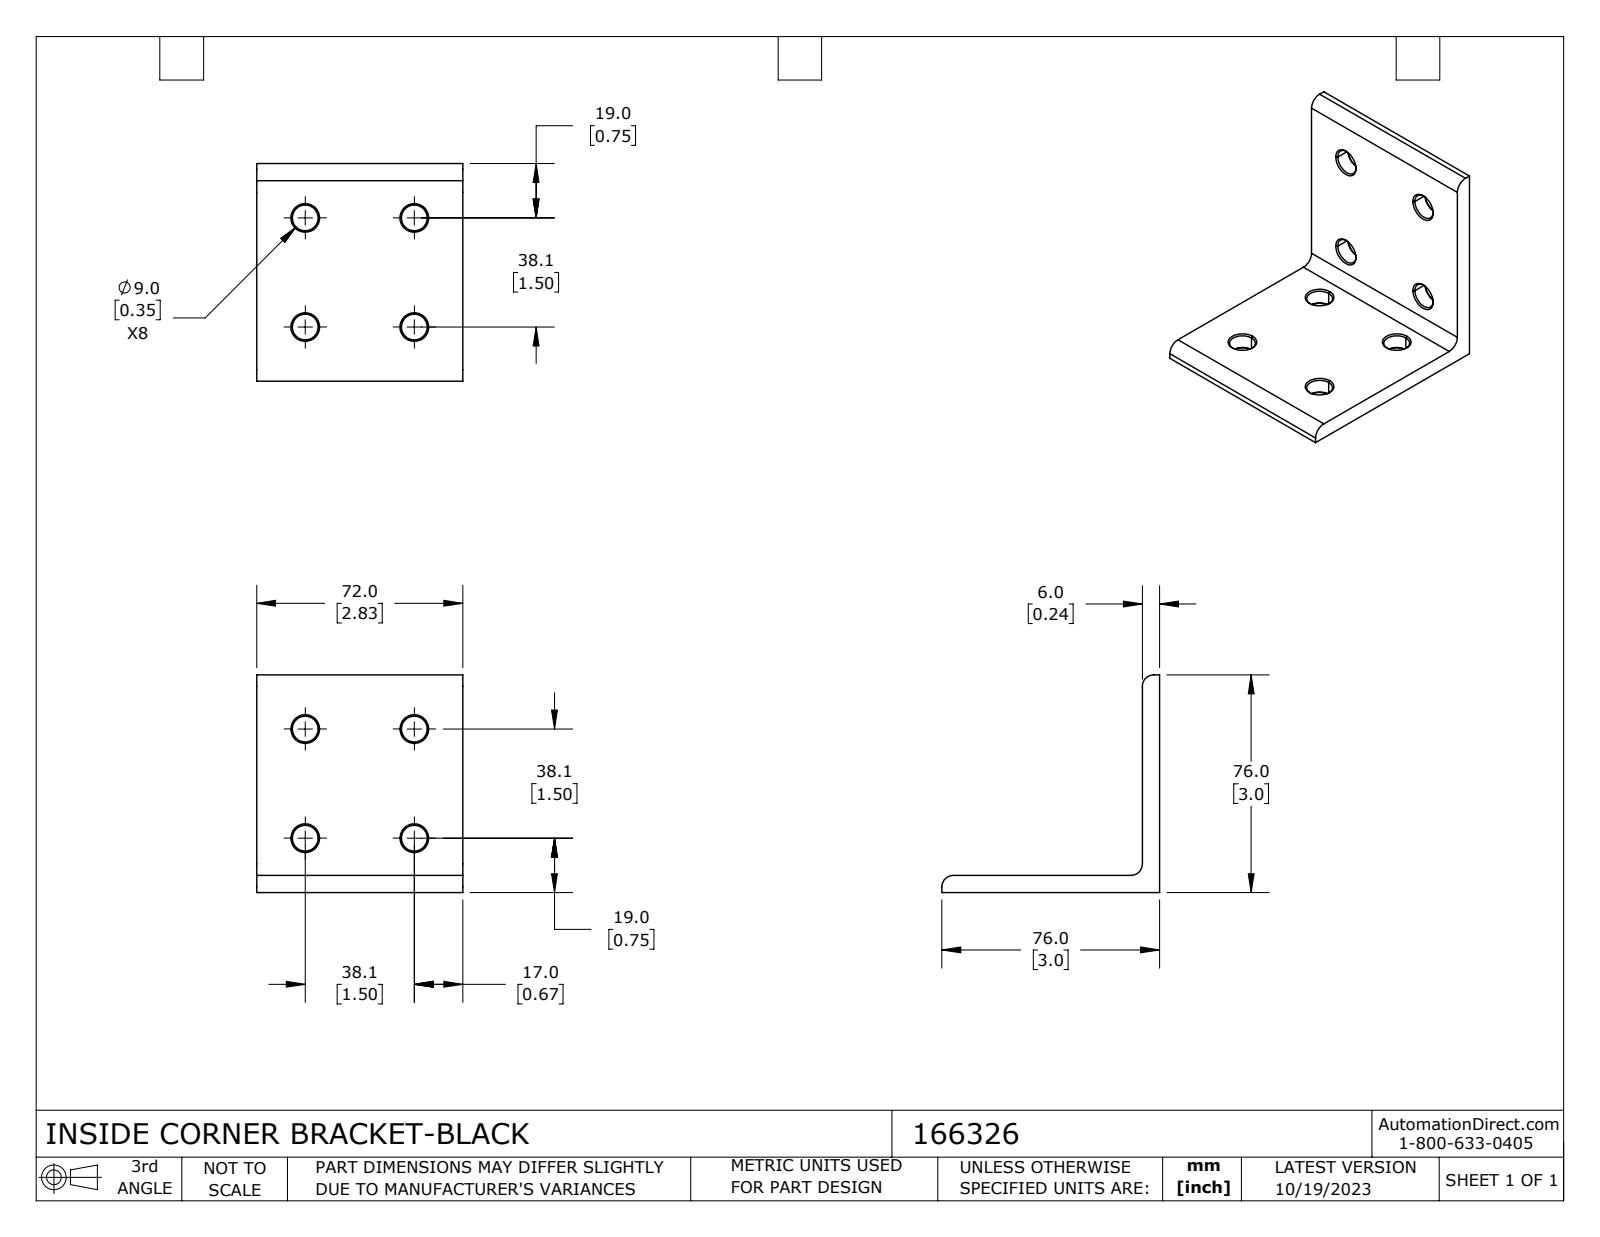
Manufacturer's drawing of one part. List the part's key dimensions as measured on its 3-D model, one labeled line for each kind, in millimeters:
Part name (STEP PRODUCT): 166326
STEP written by: SolidWorks 2023 (CONFIG_CONTROL_DESIGN)
Units: millimetres
Bodies: 1 solid, 59 faces (8 planar, 19 cylindrical, 32 other)
Overall size (bounding box): 76 × 76 × 72
Volume: 59 713 mm³ · Surface area: 23 474 mm²
Round holes (diameter × count): ⌀9 ×8
Partial cylindrical surfaces — rounded edges, fillets, slot ends (radius × count): R4 ×3
Main face-to-face distances: 6, 72, 76, 70
Hole centre spacings: 38.1, 53.88
